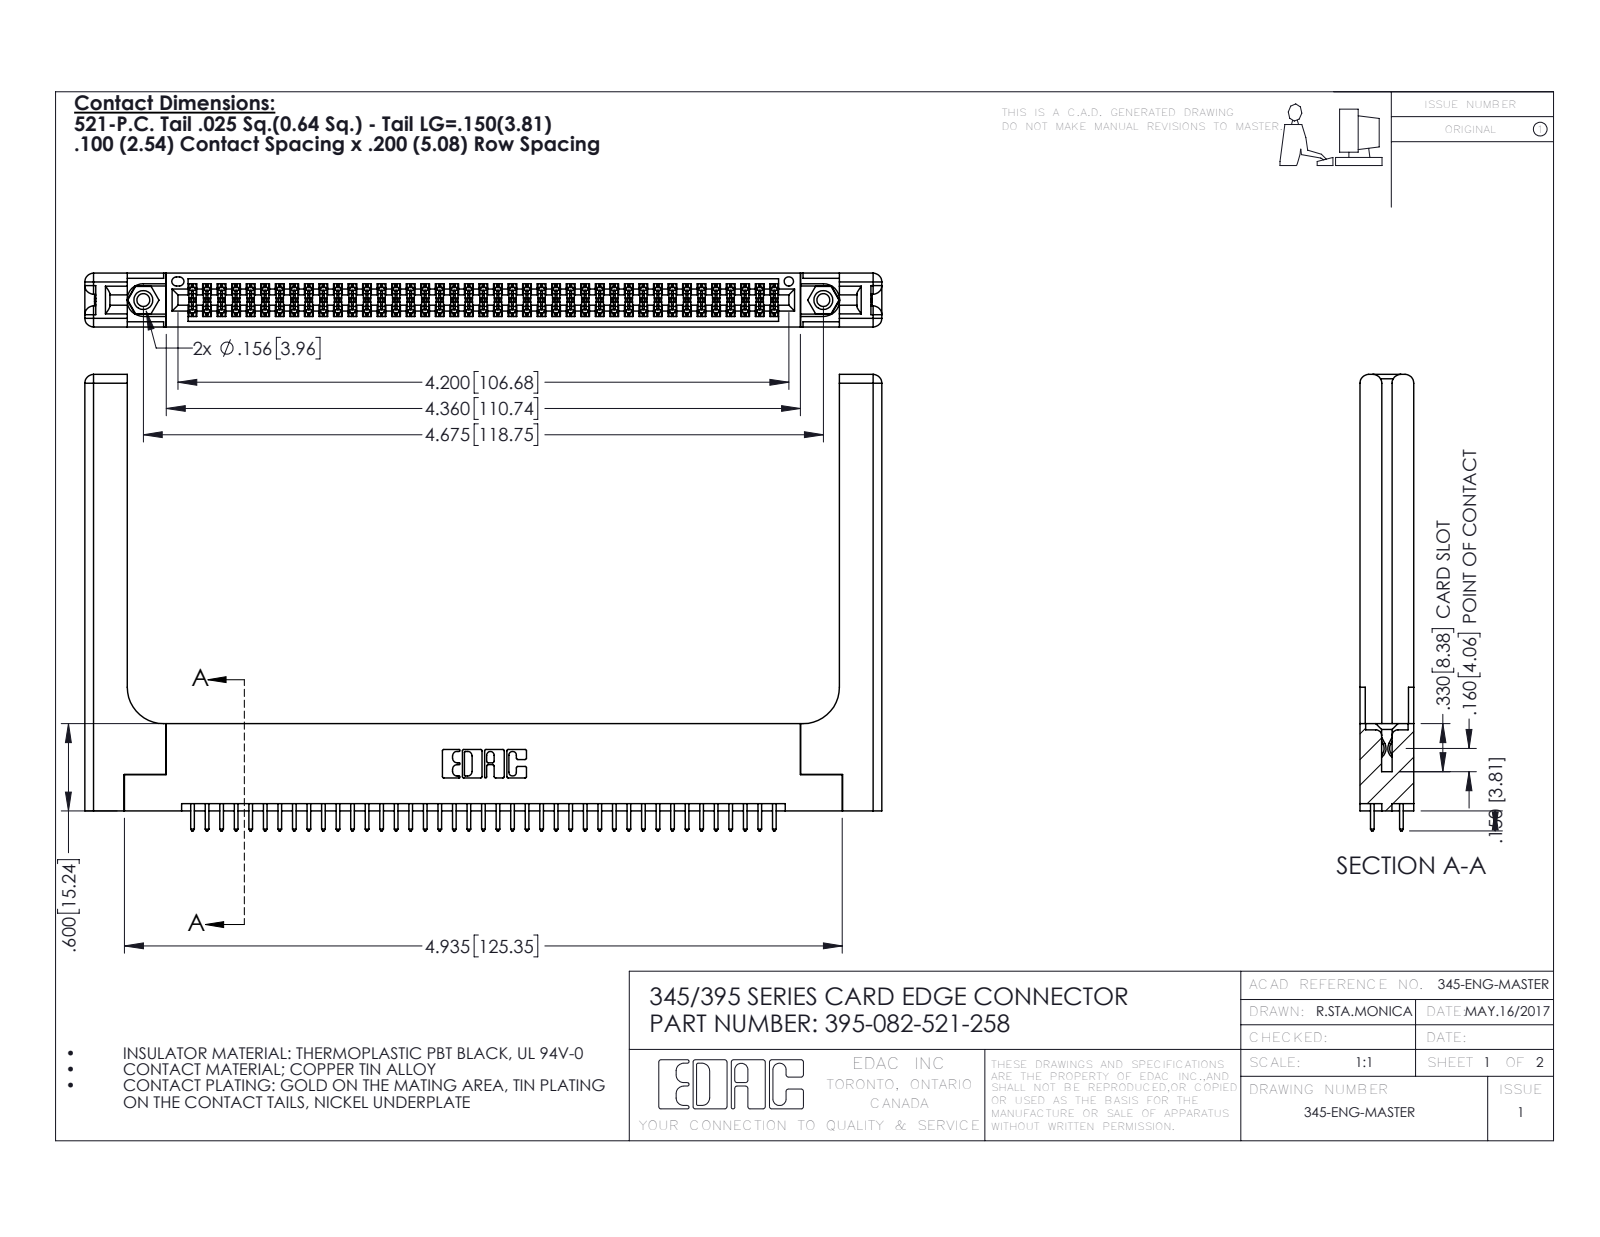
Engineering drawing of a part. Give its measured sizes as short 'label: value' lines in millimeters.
name: 345 Part_Flush Mounting Lugs - 0.156 Dia-TH; 345-220-058_345-220-058; 395-082-521-258; 345-292-001_345-293-121 (+1 more)
written by: SolidWorks 2016 (CONFIG_CONTROL_DESIGN)
unit: mm
bodies: 87 solids, 4482 faces (2934 planar, 1488 cylindrical, 60 other)
size: 139.2 × 79.7 × 9.4
volume: 21 960 mm³; area: 24 740 mm²
holes: 2× ⌀2.3, 2× ⌀3.2, 2× ⌀4, 1× ⌀1.6
bosses: 2× ⌀3.9
rounds: 123× R0.2, 82× R0.3, 22× R0.3, 16× R1.5, 6× R0.2, 6× R0.8, 3× R0.7, 2× R0.4
face distances: 1.8, 7.6, 9.4, 5.1, 2.5, 6.9, 0.6, 5.7, 3.8, 3.8
hole spacings: 6.9, 112.8, 118.7
